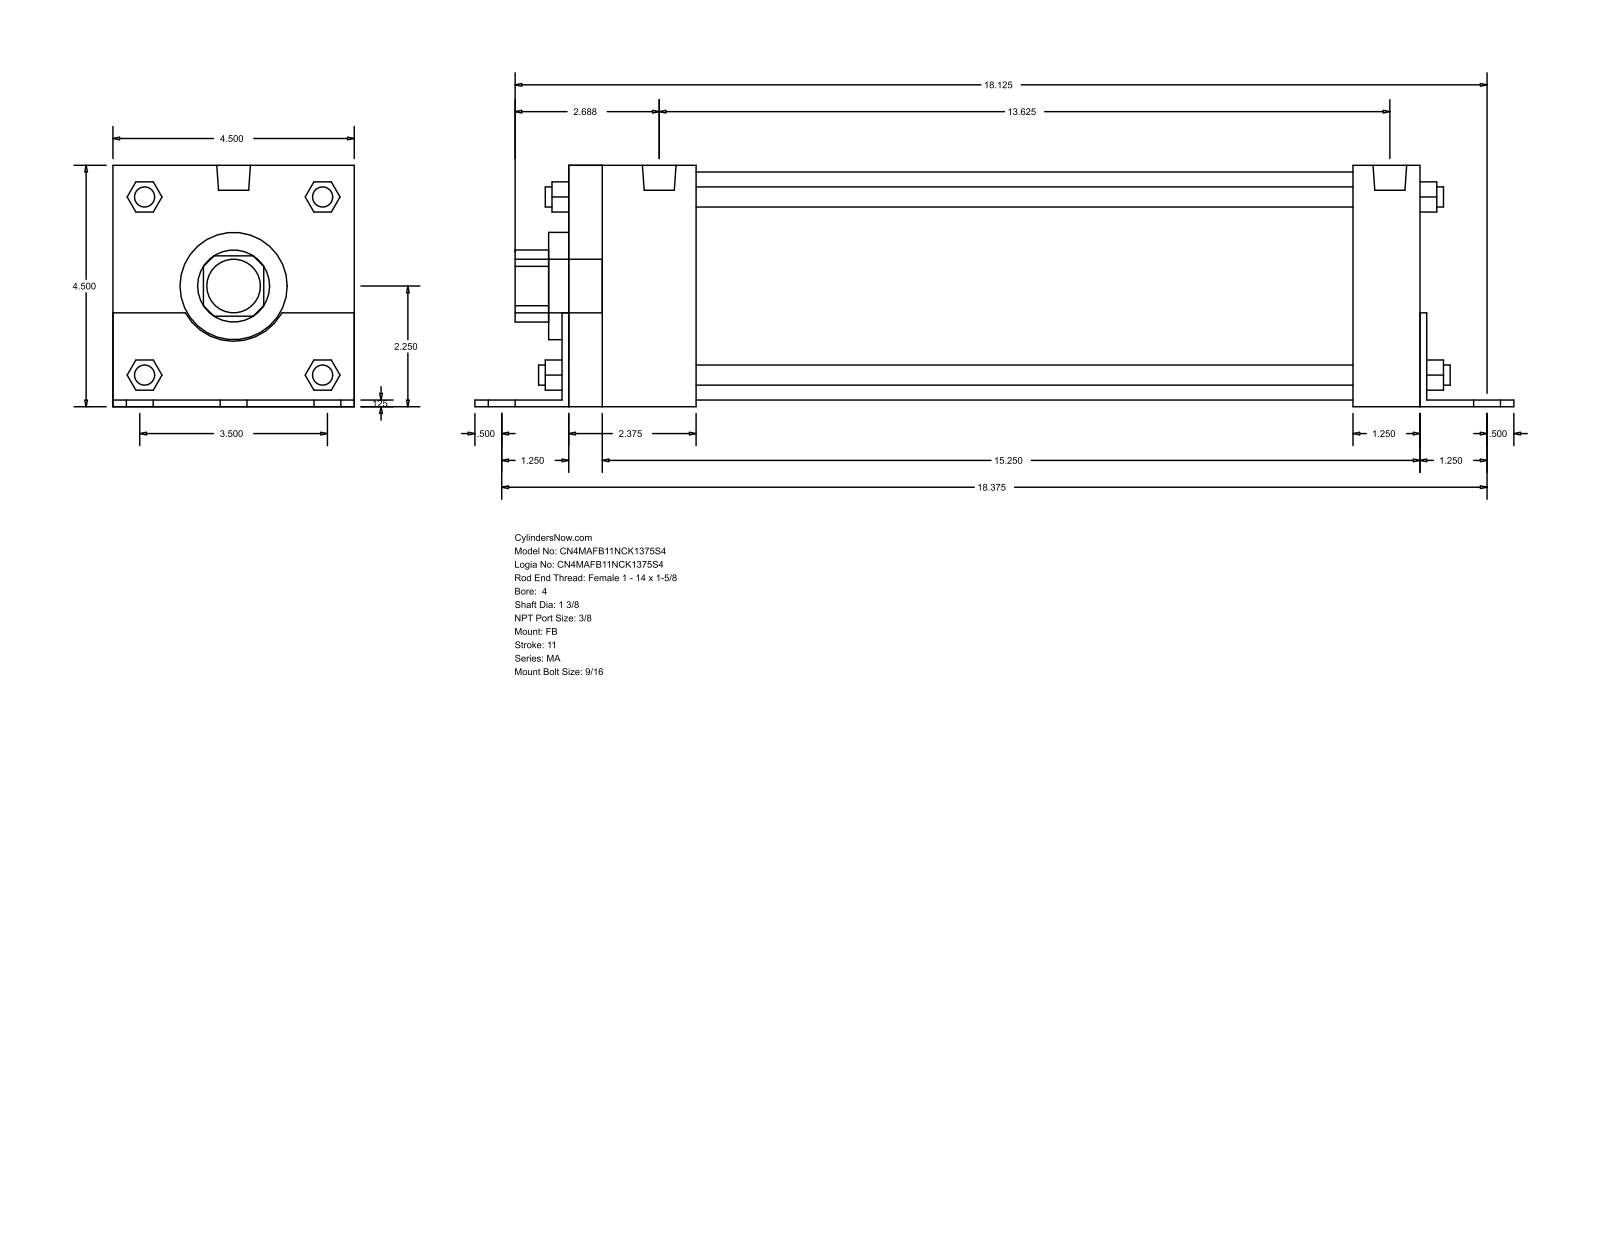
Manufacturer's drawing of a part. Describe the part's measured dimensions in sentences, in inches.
The part is named "MA_FB__0400_1.375". Its 3-D file was written by "GSSL Pune (CONFIG_CONTROL_DESIGN)". It is 0 solids with 140 faces: 105 planar, 35 cylindrical and 0 other. Overall it measures 19.375 by 4.502 by 4.5 inches. Round holes: 1 of diameter 1.375, 1 of diameter 2, 1 of diameter 4.25. Round bosses or shafts: 6 of diameter 0.563, 4 of diameter 0.437, 4 of diameter 0.375, 2 of diameter 0.627, 1 of diameter 1. Partial cylindrical surfaces (rounded edges, fillets, slot ends): 1 of radius 0.672, 1 of radius 1.03. The main face-to-face distances are 4.5, 0.125, 4.502, 0.123, 4.377, 15.875, 0.125, 16, 2.375, 16.
